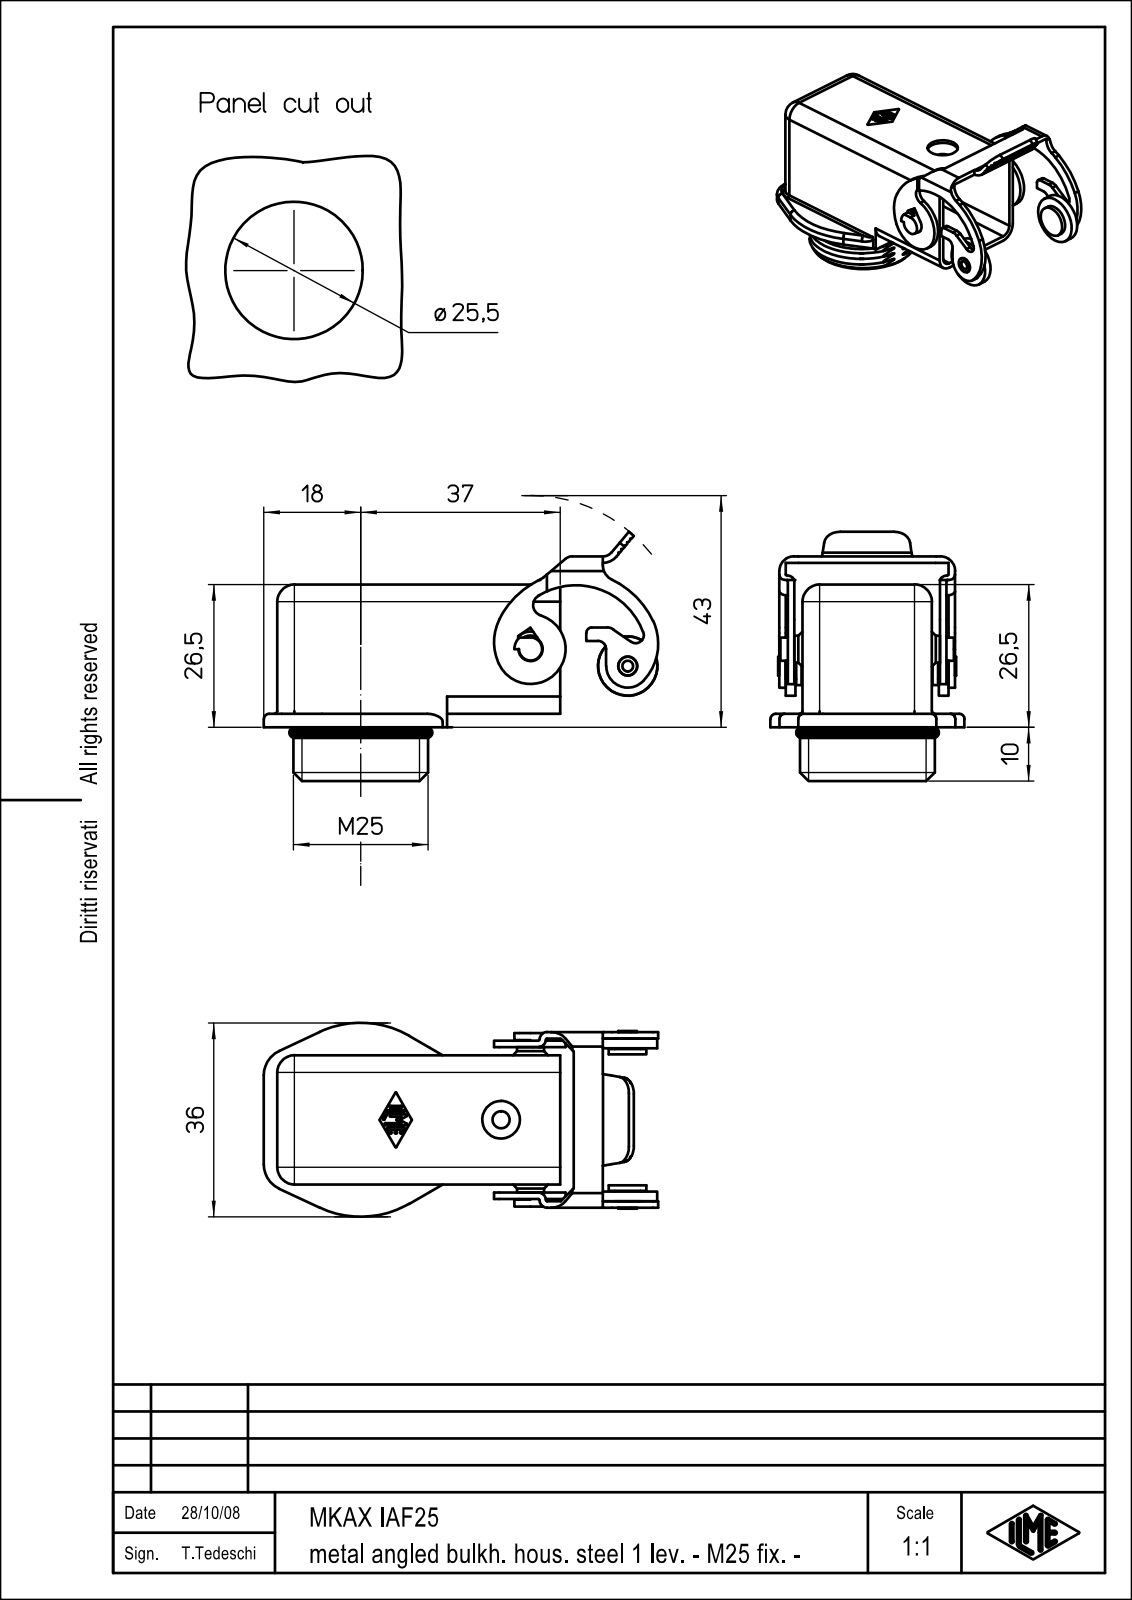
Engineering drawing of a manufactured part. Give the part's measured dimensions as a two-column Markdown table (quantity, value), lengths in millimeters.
| quantity | value |
| --- | --- |
| part name | LEVA; CUSTODIA; MKAX_IAF25 |
| STEP written by | CoCreate Modeling 16.00A 16-Aug-2008 (C) Parametric Technology GmbH (AUTOMOTIVE_DESIGN) |
| units | millimeters |
| bodies | 2 solids, 346 faces (148 planar, 167 cylindrical, 31 other) |
| overall size | 73.16 × 46.3 × 36 |
| volume | 11 388 mm³ |
| surface area | 15 187 mm² |
| round holes (diameter × count) | 2 × 1, 3.2 × 1, 5 × 1, 7 × 1 |
| round bosses / shafts (diameter × count) | 22.8 × 1, 11 × 1, 7 × 1, 5 × 1, 4.8 × 1, 4.3 × 1, 3.5 × 1 |
| partial cylindrical surfaces (radius × count) | 0.2 × 15, 2 × 12, 3.2 × 8, 1 × 6, 0.5 × 5, 3 × 5, 1.4 × 4, 0.1 × 3 |
| main face-to-face distances | 24, 1.2, 26.5, 2.5, 1.5, 29.8, 1.6, 25.5, 4.3, 28.3 |
